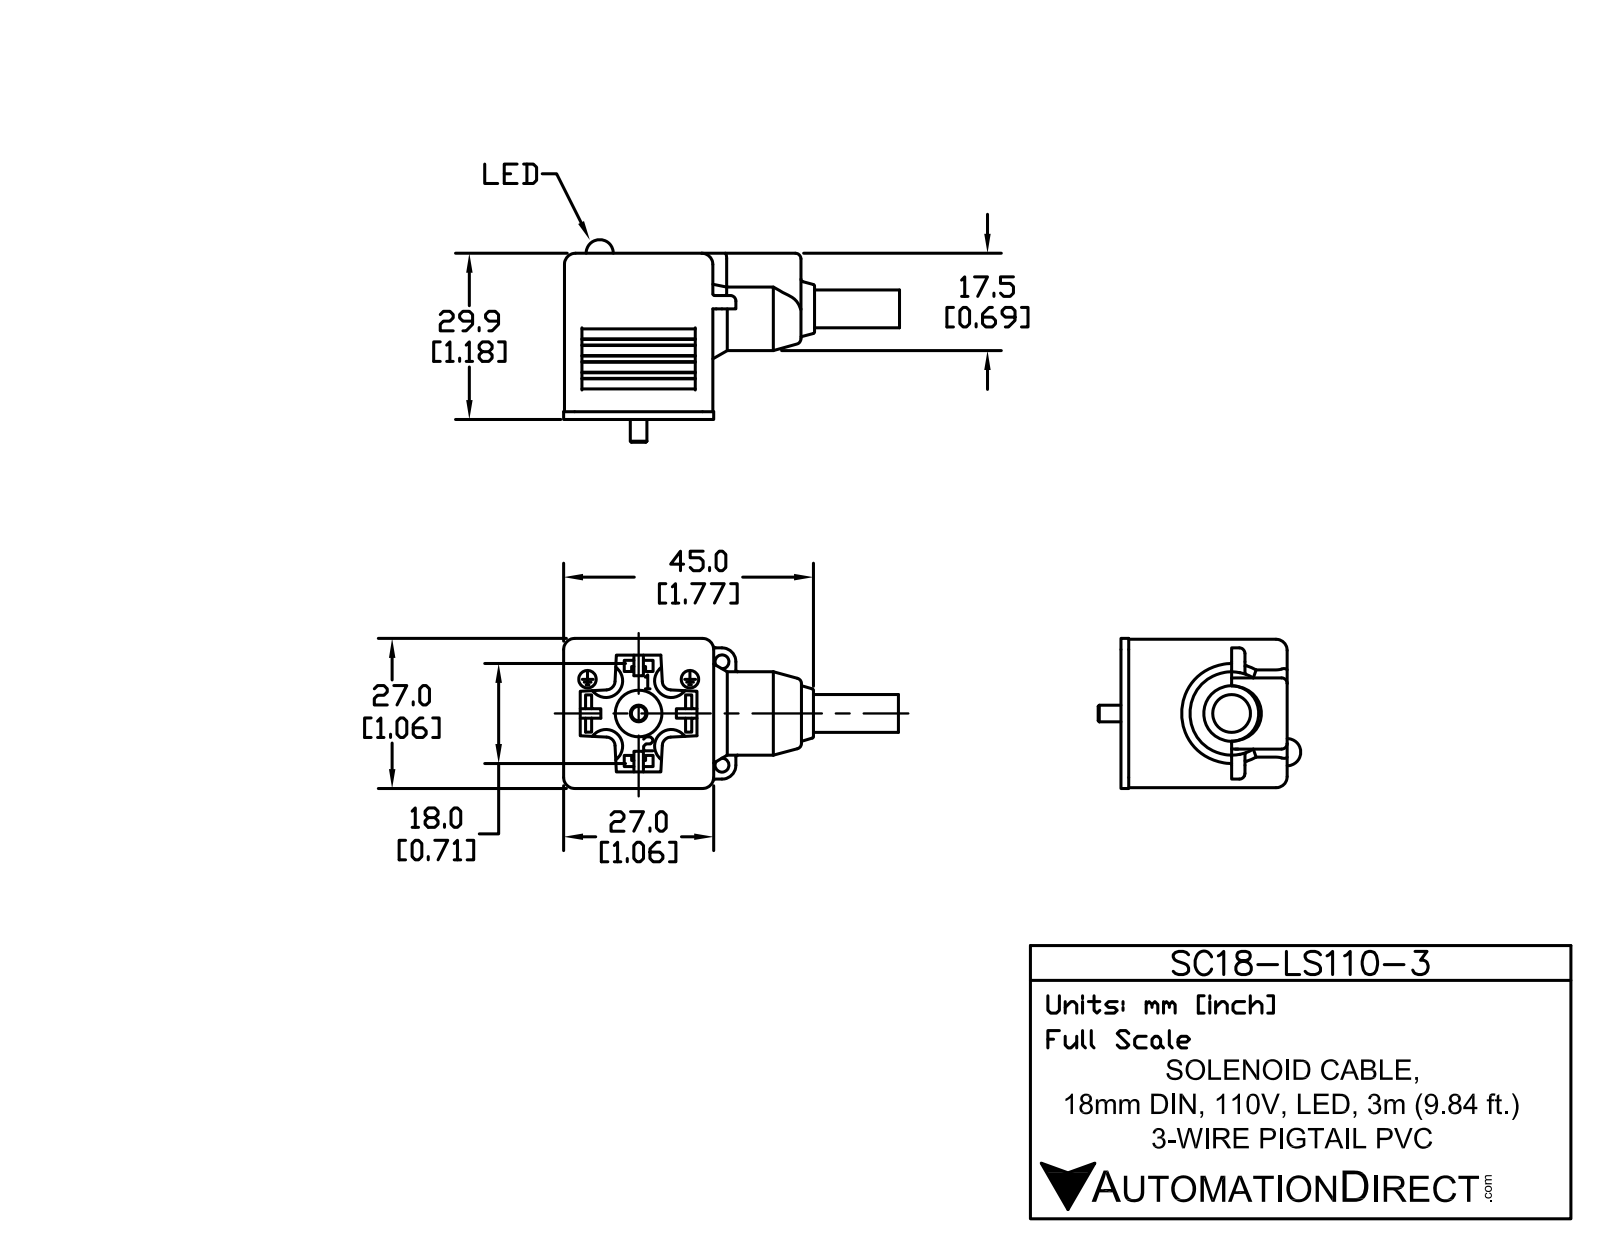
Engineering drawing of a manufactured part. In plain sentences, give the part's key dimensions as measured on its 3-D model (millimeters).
The part is named "SC18-LS110-3". Its 3-D file was written by "SolidWorks 2011 (AUTOMOTIVE_DESIGN)". It is 5 solids with 269 faces: 210 planar, 34 cylindrical and 25 other. Overall it measures 73.26 by 36.01 by 27 millimeters. Its volume is 22 295 cubic millimeters and its surface area 8 255 square millimeters. Round holes: 2 of diameter 2.25, 2 of diameter 6, 1 of diameter 4, 1 of diameter 8.4. Round bosses or shafts: 1 of diameter 5.75, 1 of diameter 3, 1 of diameter 2.75. Partial cylindrical surfaces (rounded edges, fillets, slot ends): 11 of radius 1, 4 of radius 2, 4 of radius 3, 1 of radius 7.5. The main face-to-face distances are 23.24, 27, 2, 25.24, 1, 22.24, 24.24, 26.7, 20, 7. The hole center spacings are 5.87, 5.9, 11.77.
